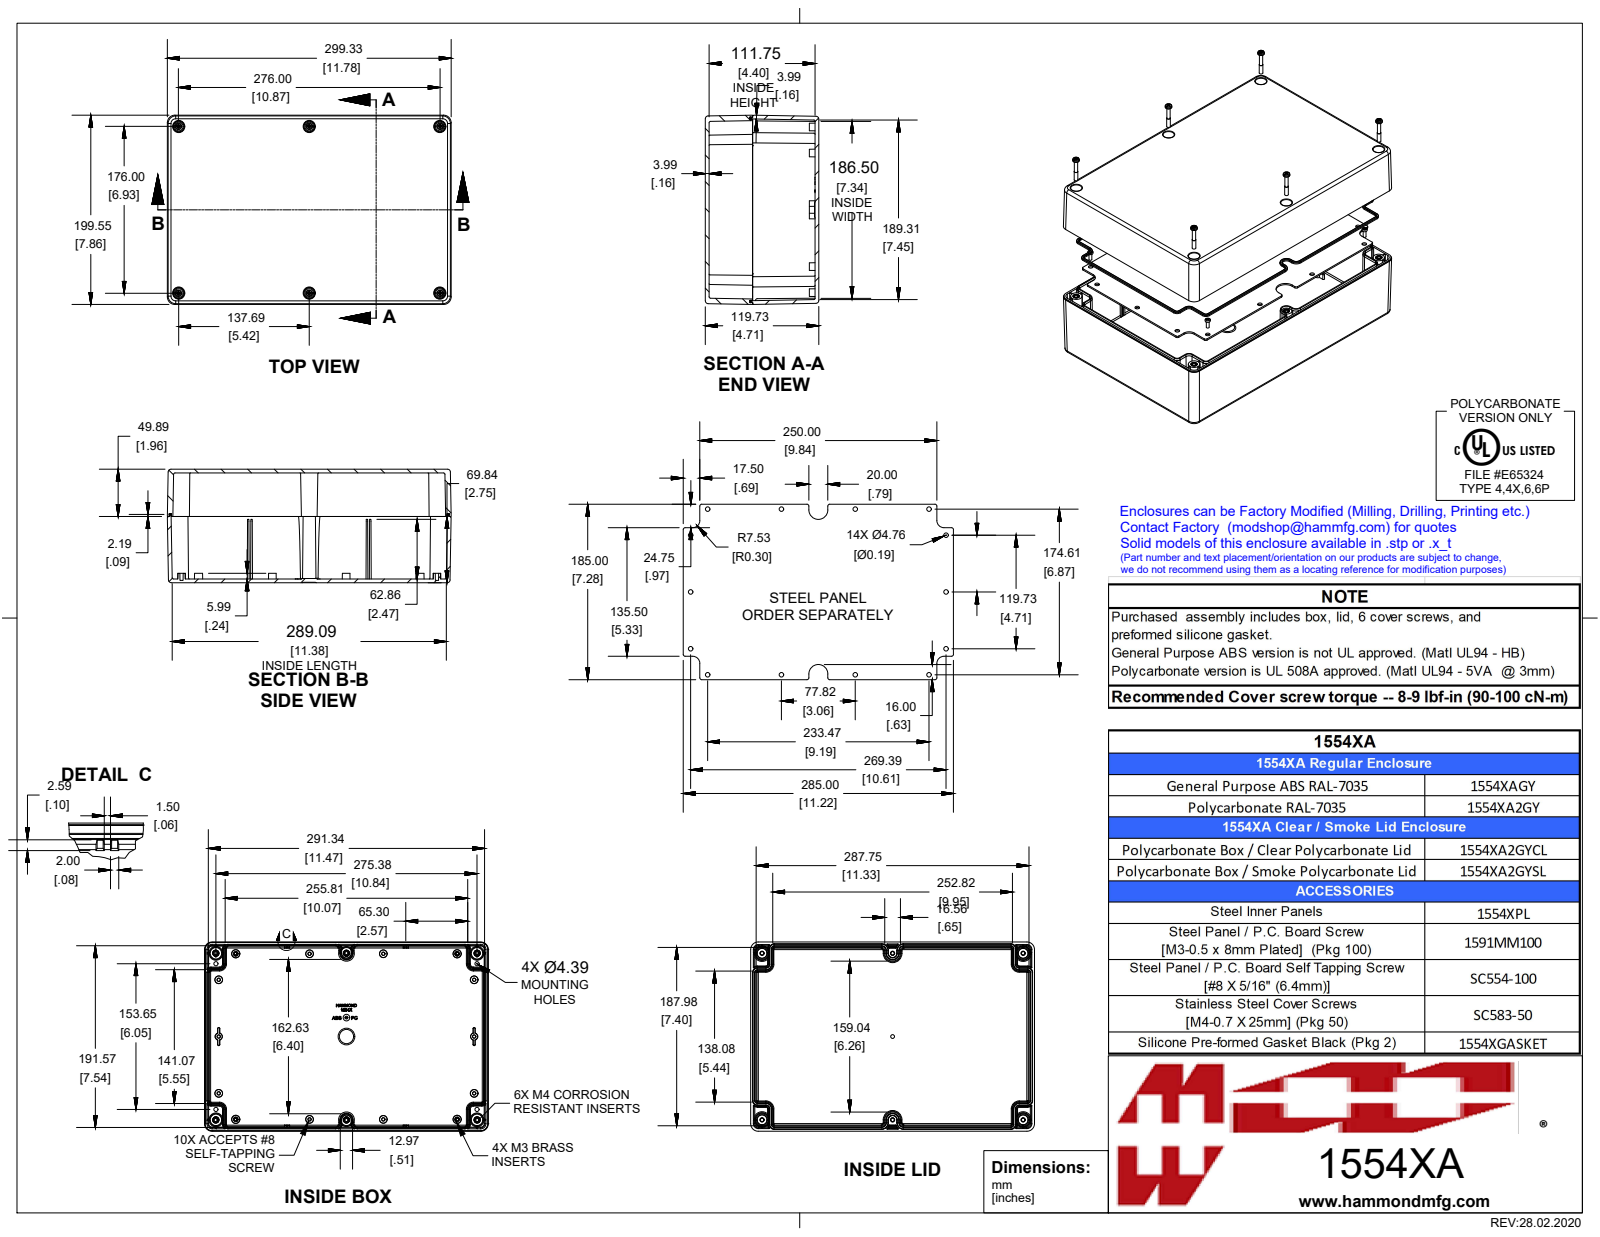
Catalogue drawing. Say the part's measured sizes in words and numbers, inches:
The part is named "1554XAGY". Its 3-D file was written by "SolidWorks 2019 (AUTOMOTIVE_DESIGN)". It is 24 solids with 3245 faces: 935 planar, 720 cylindrical and 1590 other. Overall it measures 11.811 by 7.874 by 4.724 inches. Its volume is 69.84 cubic inches and its surface area 1 036 square inches. Round holes: 14 of diameter 0.187, 6 of diameter 0.128, 6 of diameter 0.142, 4 of diameter 0.097, 1 of diameter 0.276. Round bosses or shafts: 6 of diameter 0.272, 6 of diameter 0.25, 6 of diameter 0.213, 6 of diameter 0.21, 6 of diameter 0.152, 6 of diameter 0.137, 5 of diameter 0.118, 4 of diameter 0.19. Partial cylindrical surfaces (rounded edges, fillets, slot ends): 30 of radius 0.02, 20 of radius 0.012, 14 of radius 0.079, 12 of radius 0.031, 12 of radius 0.118, 8 of radius 0.028, 8 of radius 0.047, 8 of radius 0.315. The main face-to-face distances are 0.157, 4.567, 4.724, 0.236, 0.394, 4.331, 4.409, 4.173, 0.064, 0.458. The hole center spacings are 3.071, 7.543, 0.827, 1.109, 1.294, 1.535, 2.362, 3.467.
